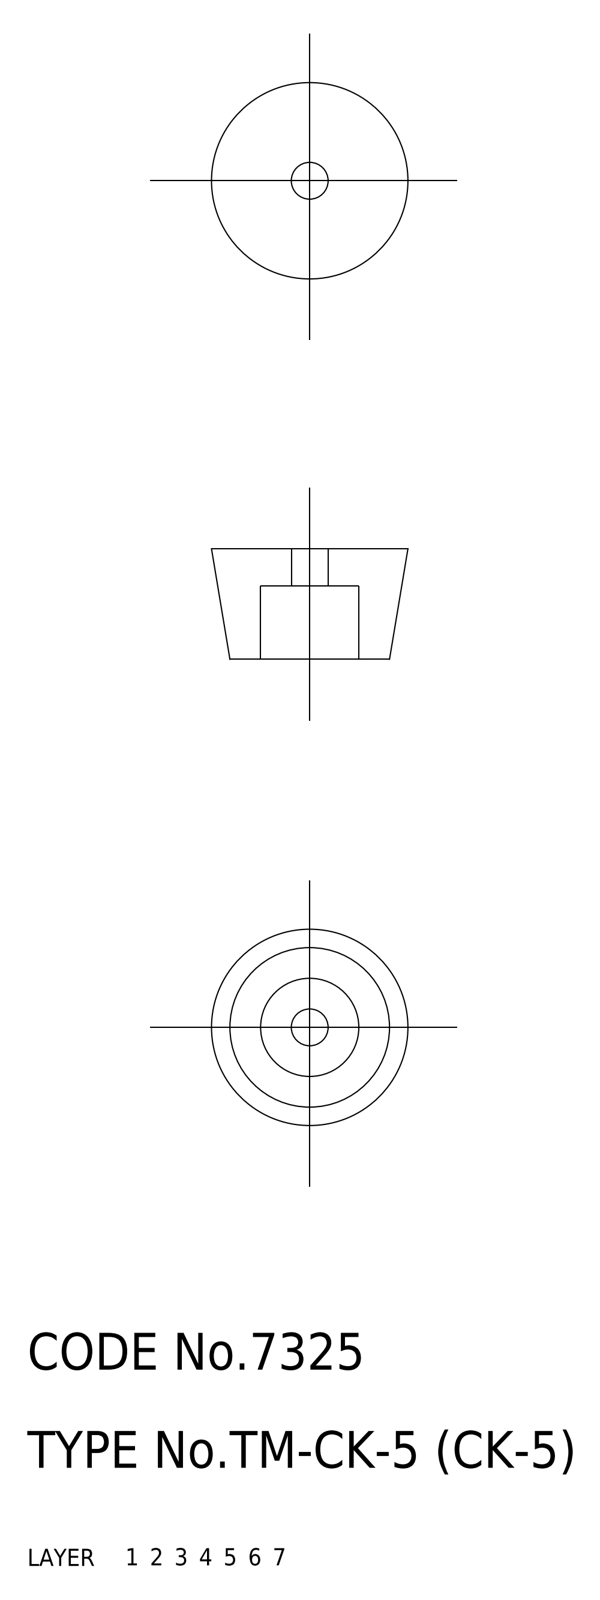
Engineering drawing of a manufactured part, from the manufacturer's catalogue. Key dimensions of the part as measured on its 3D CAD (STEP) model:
Part name (STEP PRODUCT): washer; rubber foot; CK_5_1163_36
STEP written by: CADfix (AUTOMOTIVE_DESIGN)
Units: millimetres
Bodies: 2 solids, 21 faces (0 planar, 0 cylindrical, 21 other)
Overall size (bounding box): 16 × 16 × 9
Volume: 1 171 mm³ · Surface area: 1 164 mm²
